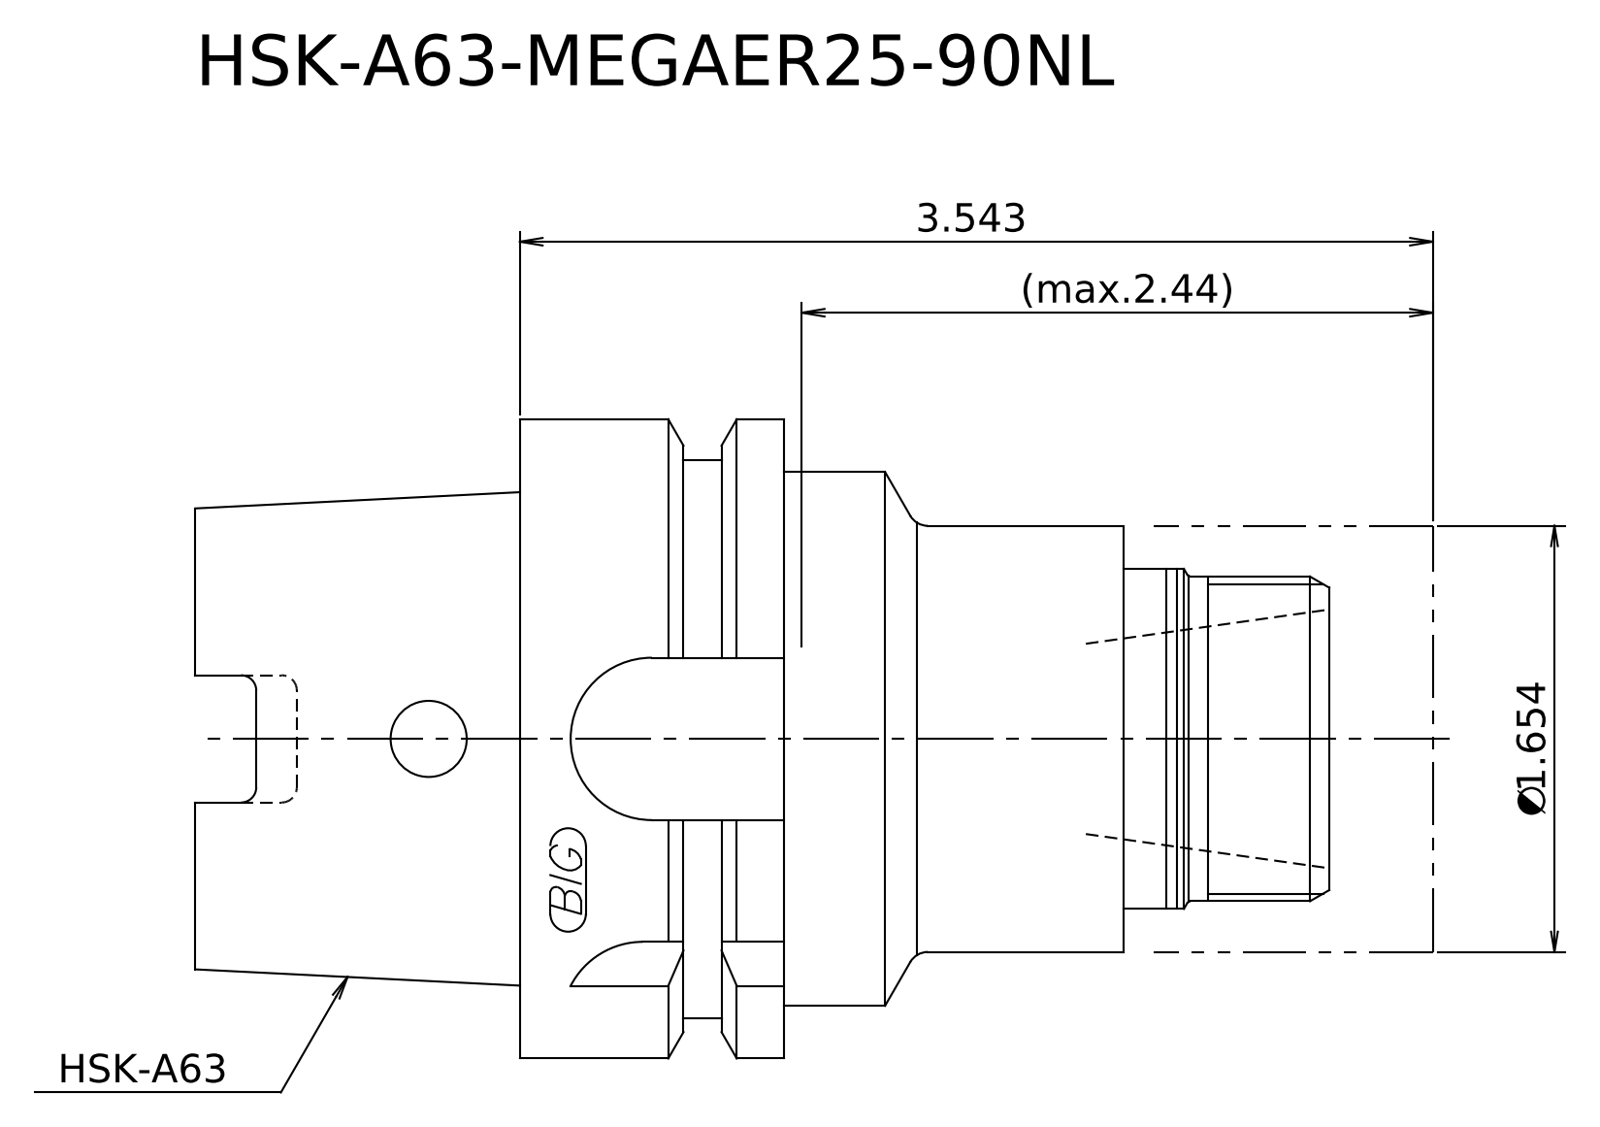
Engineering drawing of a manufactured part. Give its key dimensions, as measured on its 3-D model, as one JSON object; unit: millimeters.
{"step_written_by": "Kubotek KeyCreator 2011 V10.0.2 (22737) (automotive_design)", "units": "millimeters", "bodies": {"solids": 2, "faces": 23, "planar": 9, "cylindrical": 8, "other": 6}, "overall_size": [122, 63, 63], "volume_mm3": 243812, "surface_area_mm2": 29592, "round_bosses_or_shafts": [[63, 1], [55, 1], [52.6, 1], [42, 1], [33.5, 1], [32, 1]], "face_to_face_distances": [94.5, 27.5, 122, 90, 62.5, 32, 64, 36.5, 26, 58]}
